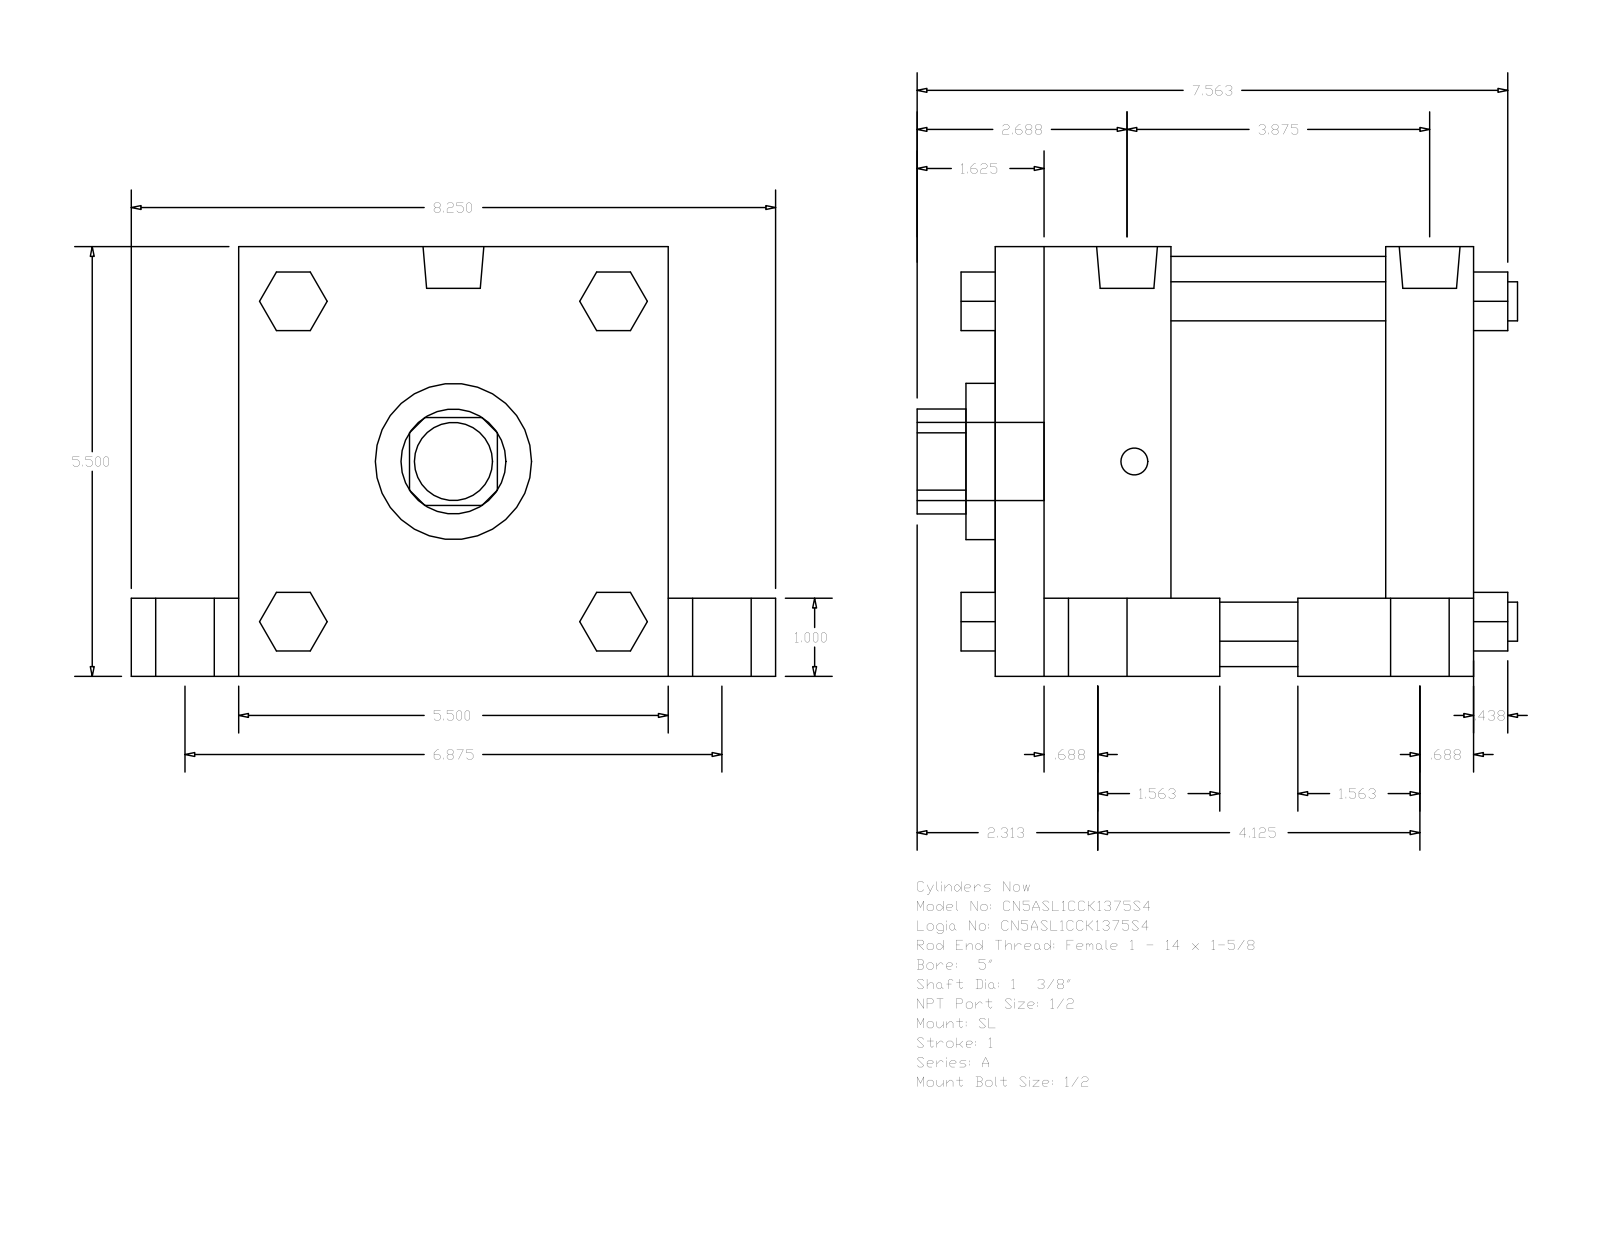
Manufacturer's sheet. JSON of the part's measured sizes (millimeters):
{"part_name": "A_SL__0500_1.375", "step_written_by": "GSSL Pune (CONFIG_CONTROL_DESIGN)", "units": "millimeters", "bodies": {"solids": 0, "faces": 150, "planar": 114, "cylindrical": 36, "other": 0}, "overall_size": [209.55, 195.26, 139.7], "round_holes": [[34.92, 1], [50.8, 1], [133.35, 1]], "round_bosses_or_shafts": [[25.4, 5], [19.05, 4], [12.7, 4], [8.73, 4], [19.77, 2]], "partial_cylinders_radius": [[17.06, 1]], "face_to_face_distances": [139.7, 155.57, 28.57, 57.15, 25.4, 114.3, 34.93, 174.63, 98.42, 69.85]}
